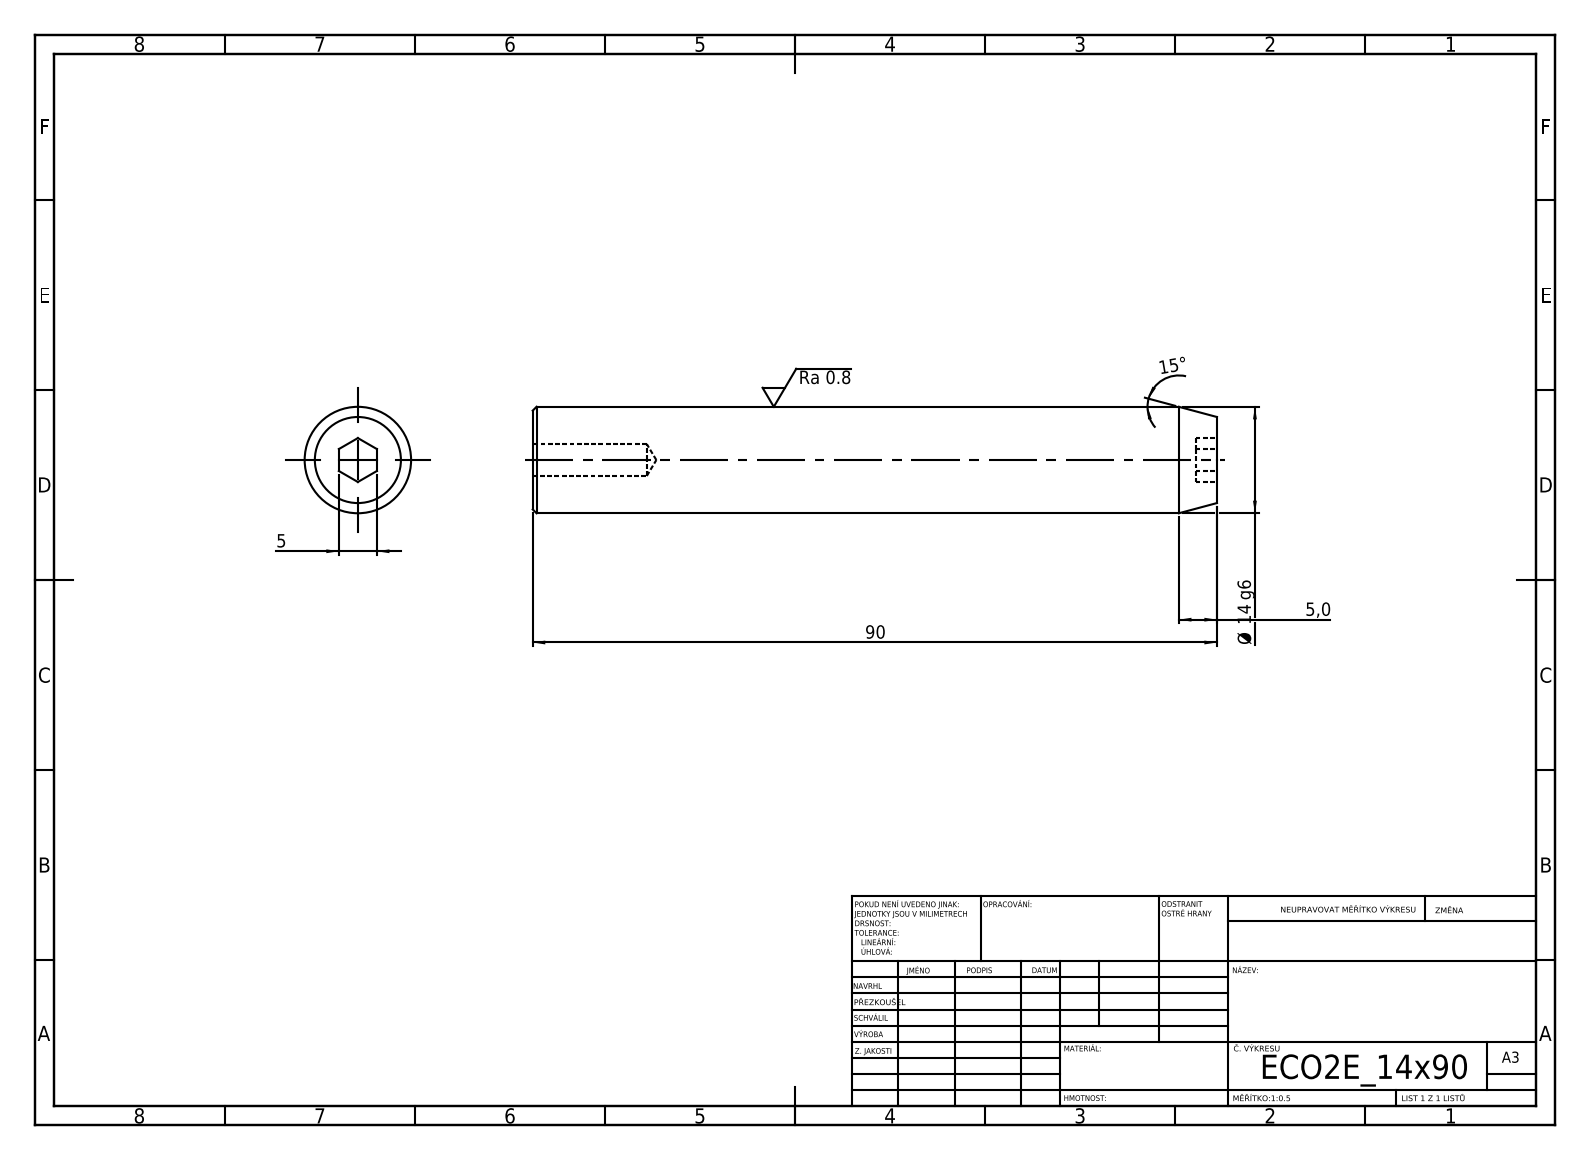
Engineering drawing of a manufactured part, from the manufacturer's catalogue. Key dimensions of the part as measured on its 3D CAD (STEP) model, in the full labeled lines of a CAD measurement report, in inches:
STEP written by: SolidWorks 2019 (CONFIG_CONTROL_DESIGN)
Units: inches
Bodies: 1 solid, 19 faces (9 planar, 4 cylindrical, 6 other)
Overall size (bounding box): 3.543 × 0.551 × 0.551
Volume: 0.82 in³ · Surface area: 6.873 in²
Round holes (diameter × count): ⌀0.165 ×1
Round bosses / shafts (diameter × count): ⌀0.551 ×1
Main face-to-face distances: 3.543, 0.197, 0.11, 3.433
